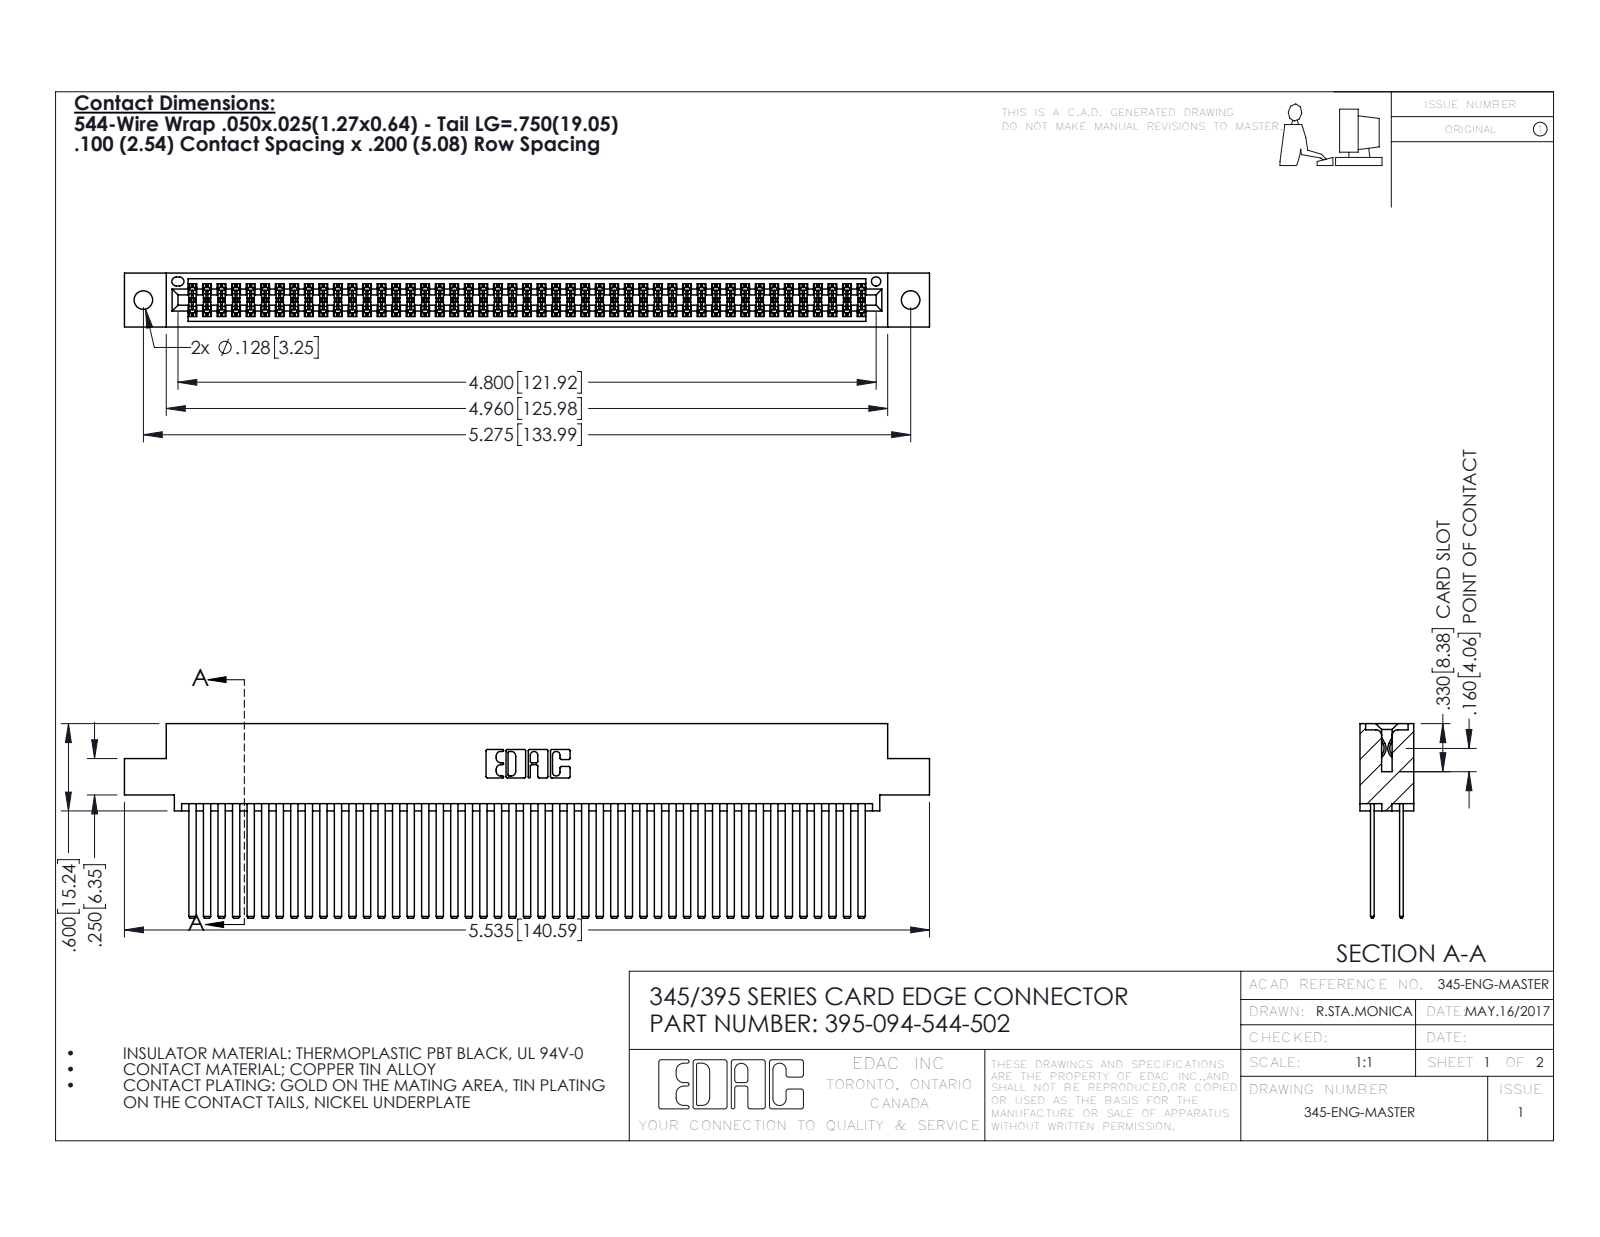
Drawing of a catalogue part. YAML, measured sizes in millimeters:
part_name: "345-292-001_345-293-144; 395-094-544-502; 345 Part_0.110 Offset - 0.128 Dia"
step_written_by: "SolidWorks 2016 (CONFIG_CONTROL_DESIGN)"
units: millimeters
bodies: {solids: 95, faces: 4266, planar: 2810, cylindrical: 1456, other: 0}
overall_size: [140.6, 34, 9.4]
volume: 14900
surface_area: 25820
round_holes:
  - {diameter: 3.3, count: 2}
  - {diameter: 1.6, count: 1}
partial_cylinders:
  - {radius: 0.2, count: 141}
  - {radius: 0.3, count: 22}
  - {radius: 0.2, count: 6}
  - {radius: 0.8, count: 6}
  - {radius: 0.7, count: 3}
  - {radius: 0.4, count: 2}
  - {radius: 0.5, count: 2}
  - {radius: 0.6, count: 2}
face_to_face_distances: [5.1, 0.6, 7.6, 1.8, 2.5, 6.9, 5.7, 4.4, 9.4, 1.3]
hole_center_spacings: [6.9, 128, 134]
